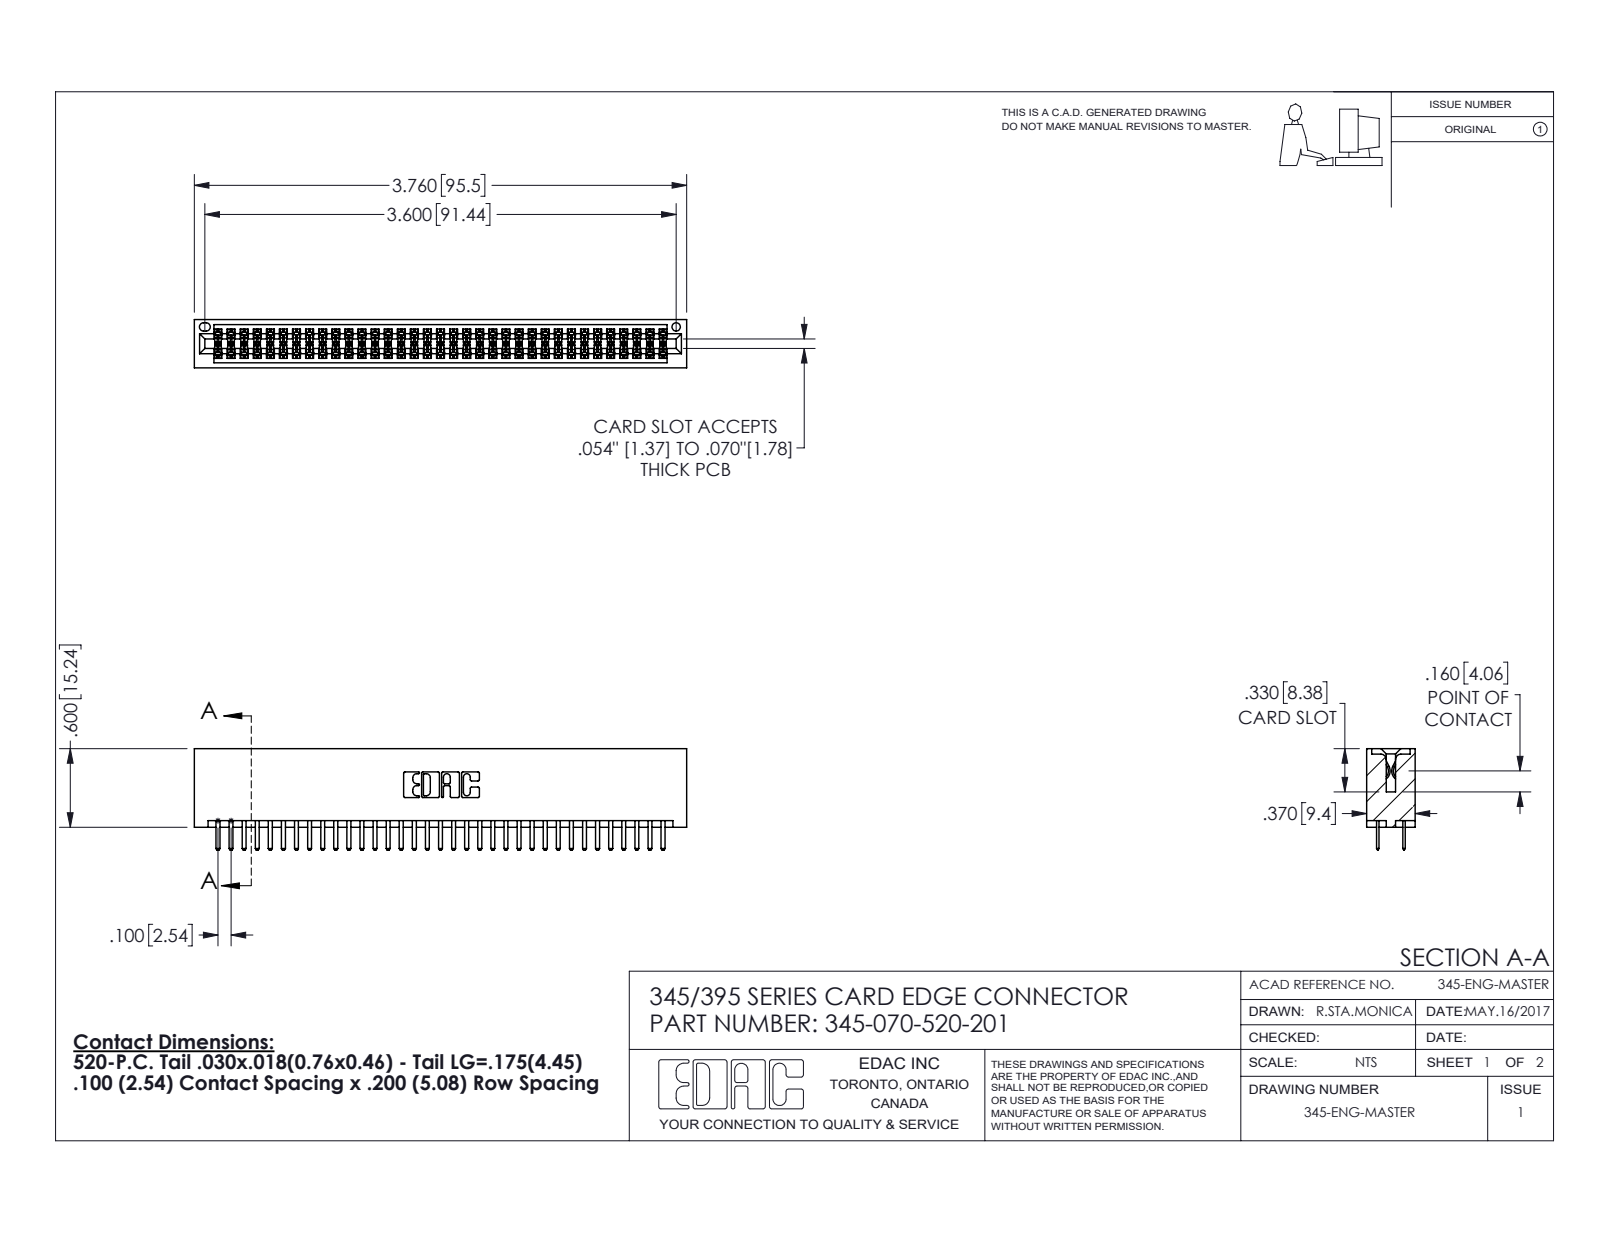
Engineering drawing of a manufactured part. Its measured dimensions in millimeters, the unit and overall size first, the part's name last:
Units: millimetres
Overall size (bounding box): 95.5 × 19.7 × 9.4
Round holes (diameter × count): ⌀1.6 ×1
Partial cylindrical surfaces — rounded edges, fillets, slot ends (radius × count): R0.2 ×105, R0.3 ×74, R0.3 ×22, R0.2 ×6, R0.8 ×6, R0.7 ×3, R0.4 ×2, R0.5 ×2
Main face-to-face distances: 7.6, 1.8, 5.1, 9.4, 2.5, 6.9, 0.6, 5.7, 0.6, 1.8
Volume: 9 800 mm³ · Surface area: 14 590 mm²
Bodies: 71 solids, 3898 faces (2526 planar, 1372 cylindrical, 0 other)
Part name (STEP PRODUCT): 345-070-520-201; 345-292-001_345-293-120; 345 Part_No Mounting Lugs
STEP written by: SolidWorks 2016 (CONFIG_CONTROL_DESIGN)
